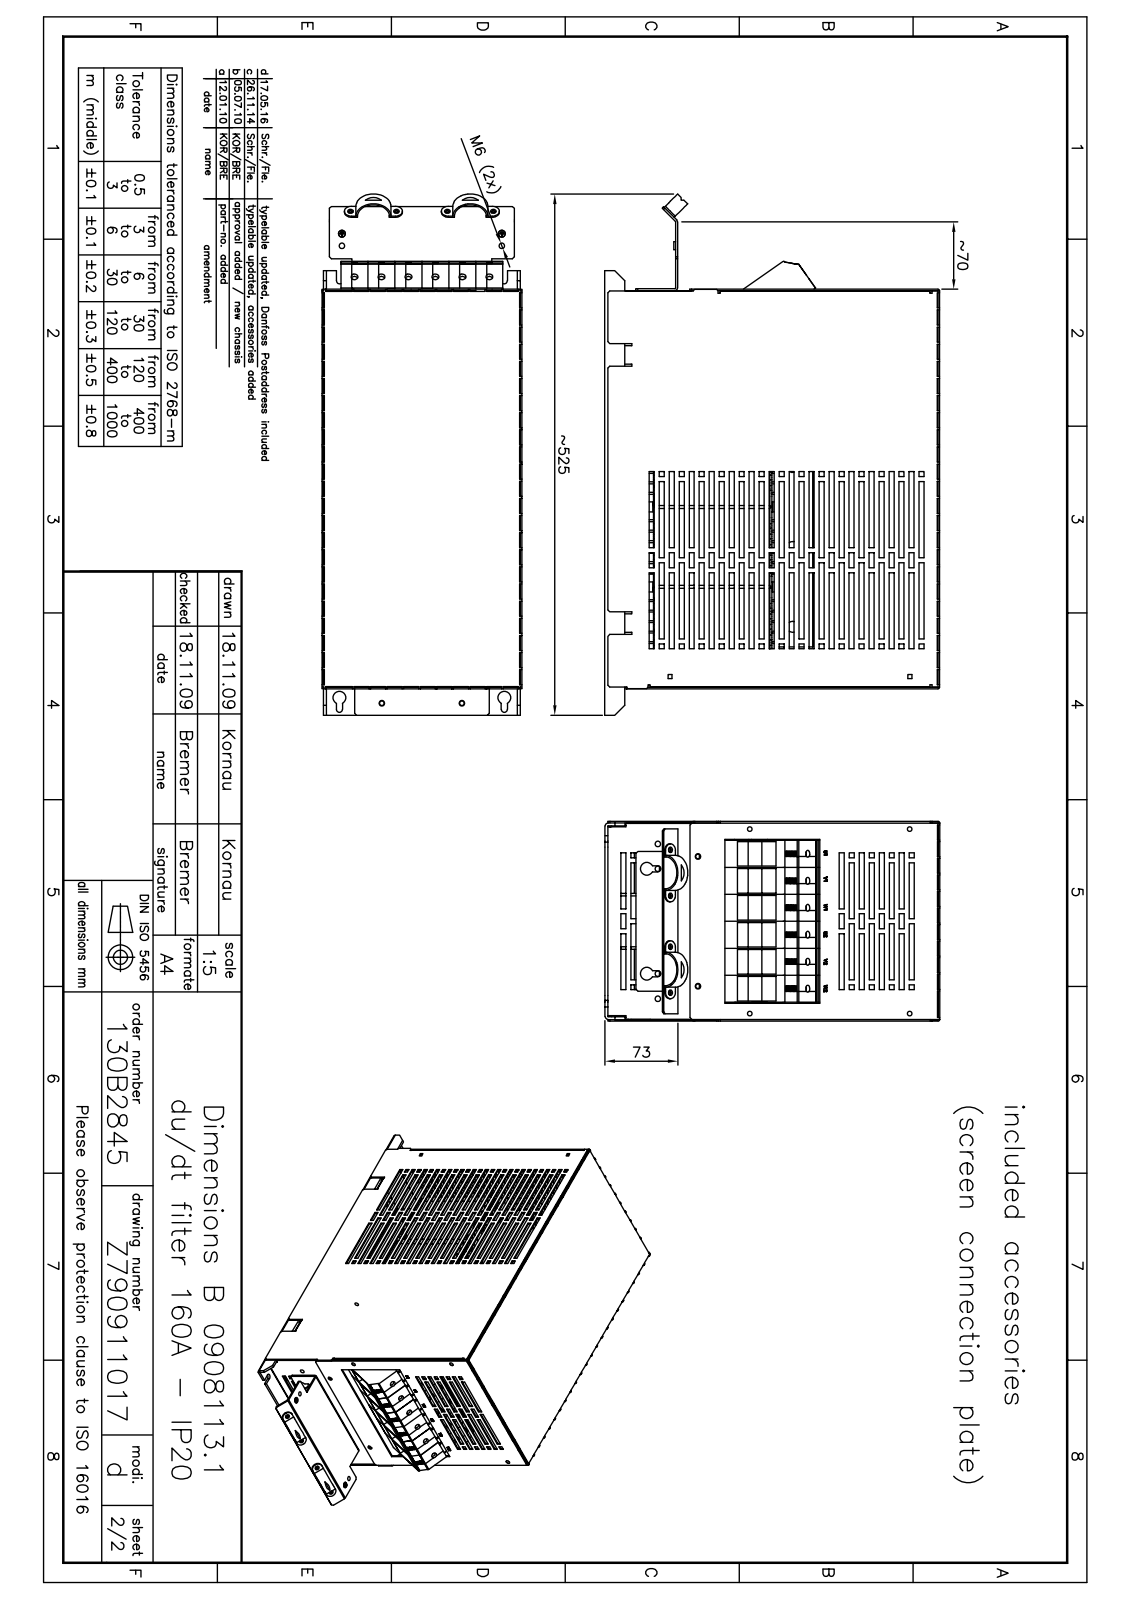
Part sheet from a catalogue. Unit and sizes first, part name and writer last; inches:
Units: inches
Overall size (bounding box): 20.545 × 13.189 × 7.874
Round holes (diameter × count): ⌀0.236 ×19, ⌀0.197 ×16, ⌀0.118 ×12, ⌀0.276 ×12, ⌀0.217 ×10, ⌀0.252 ×10, ⌀0.335 ×6, ⌀0.394 ×6, ⌀0.146 ×4, ⌀0.201 ×4, ⌀0.24 ×4, ⌀0.281 ×4
Round bosses / shafts (diameter × count): ⌀0.315 ×12, ⌀0.472 ×10, ⌀0.709 ×6, ⌀0.445 ×6, ⌀0.394 ×6, ⌀0.465 ×4, ⌀0.374 ×4, ⌀0.362 ×4
Partial cylindrical surfaces — rounded edges, fillets, slot ends (radius × count): R0.02 ×86, R0.087 ×60, R0.114 ×60, R0.004 ×33, R0.008 ×32, R0.063 ×15, R0.394 ×14, R0.787 ×12
Main face-to-face distances: 0.059, 7.815, 0.079, 2.933, 4.882, 0.118, 7.874, 2.874, 4.941, 7.756
Hole centre spacings: 3.15, 1.063, 1.819, 6.299, 2.126, 2.588, 4.51, 3.937
Volume: 322.3 in³ · Surface area: 3 422 in²
Bodies: 109 solids, 7431 faces (5447 planar, 1254 cylindrical, 730 other)
Part name (STEP PRODUCT): TS35x150_ohne Bohrungen; countersunk flat head cross recess screw_din_ISO 7046-1 - M4 x 8 - Z --- 8N; D57a; #050-0919 (+8 more)
STEP written by: SolidWorks 2014 (AUTOMOTIVE_DESIGN)
